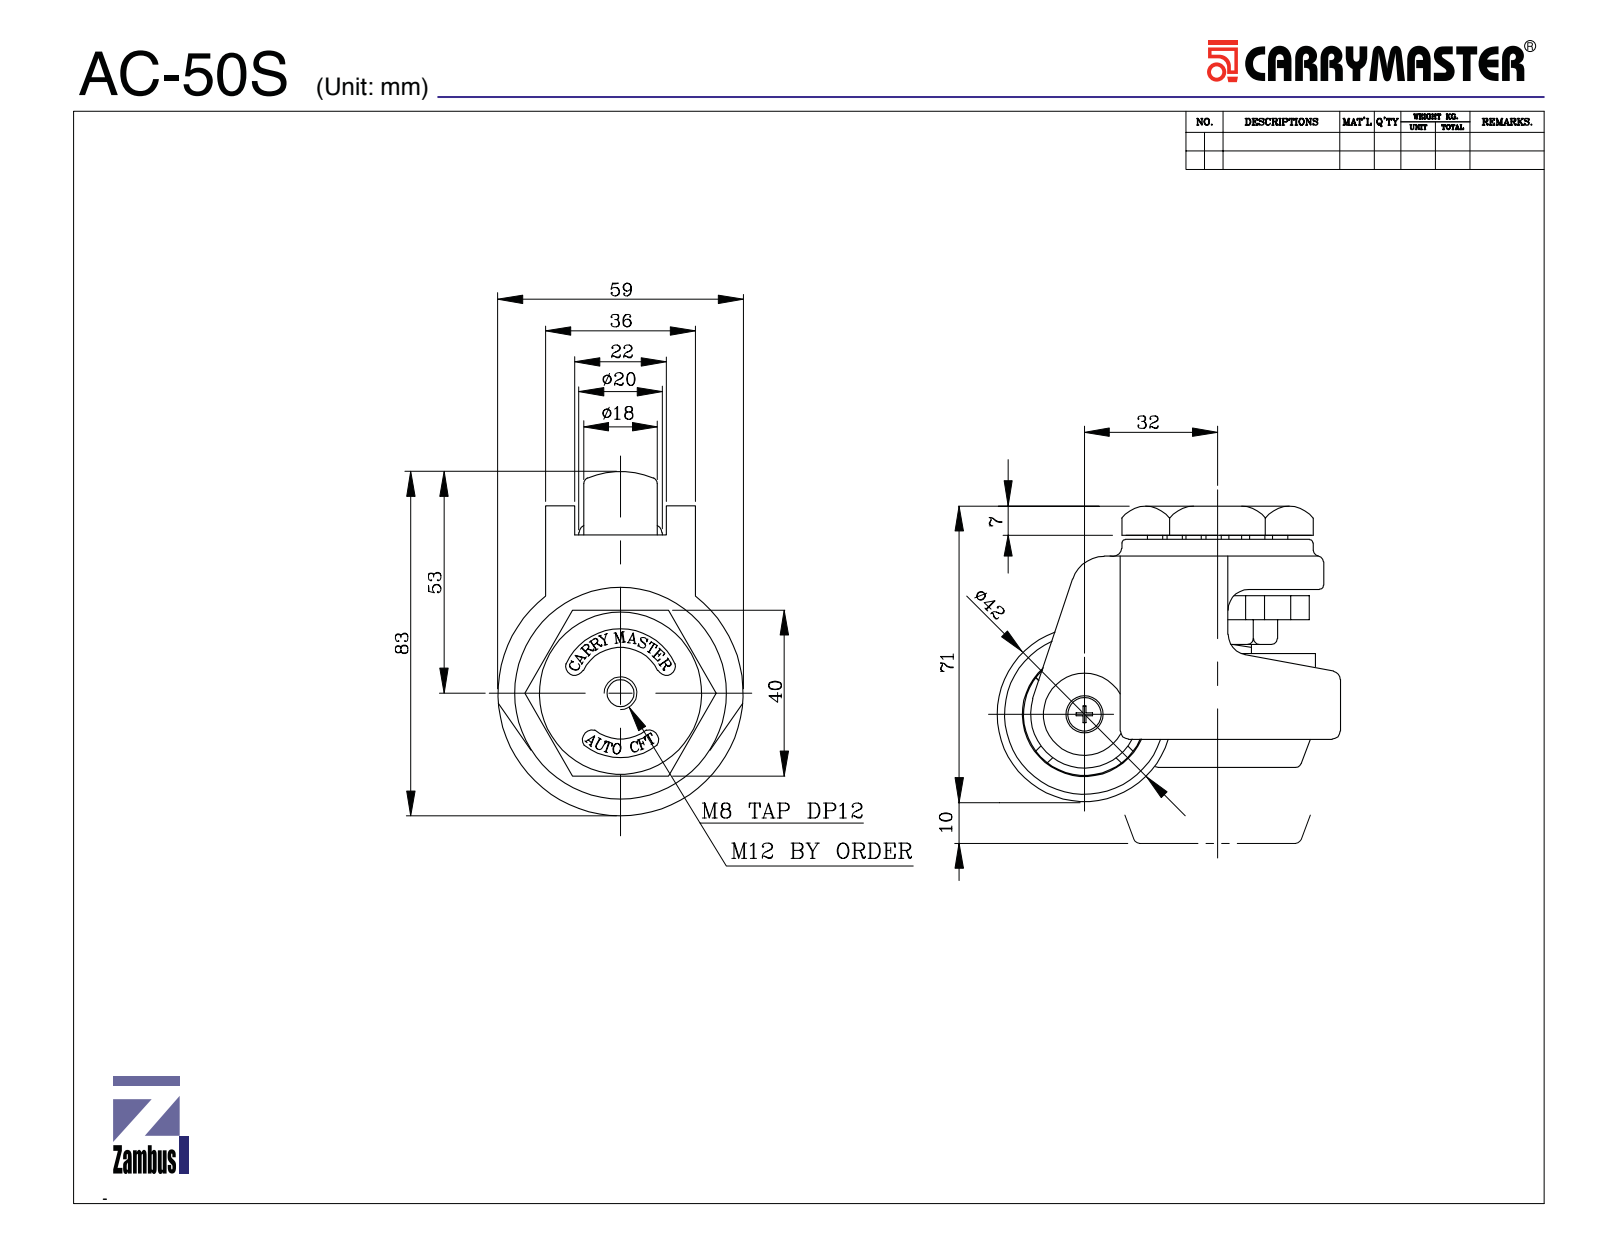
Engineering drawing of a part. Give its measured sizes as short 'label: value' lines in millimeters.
name: AC-50S
written by: SolidWorks 2015 (CONFIG_CONTROL_DESIGN)
unit: mm
bodies: 31 solids, 1126 faces (354 planar, 260 cylindrical, 512 other)
size: 82.5 × 72.2 × 61
volume: 128 209 mm³; area: 54 791 mm²
holes: 1× ⌀2.2, 1× ⌀5, 1× ⌀5.8, 1× ⌀6.8, 1× ⌀7, 1× ⌀8.2, 1× ⌀8.7, 1× ⌀16.6, 1× ⌀24, 1× ⌀25, 1× ⌀32.54, 1× ⌀42
bosses: 2× ⌀8, 2× ⌀3, 1× ⌀46, 1× ⌀18, 1× ⌀12, 1× ⌀10, 1× ⌀6, 1× ⌀5.2
rounds: 64× R1, 6× R1.5, 6× R2, 6× R2.5, 2× R5, 1× R7.5, 1× R8, 1× R8.25
face distances: 5, 7.5, 29.5, 10, 17.41, 16.21, 21.21, 1, 48.61, 38.61
hole spacings: 0.39
